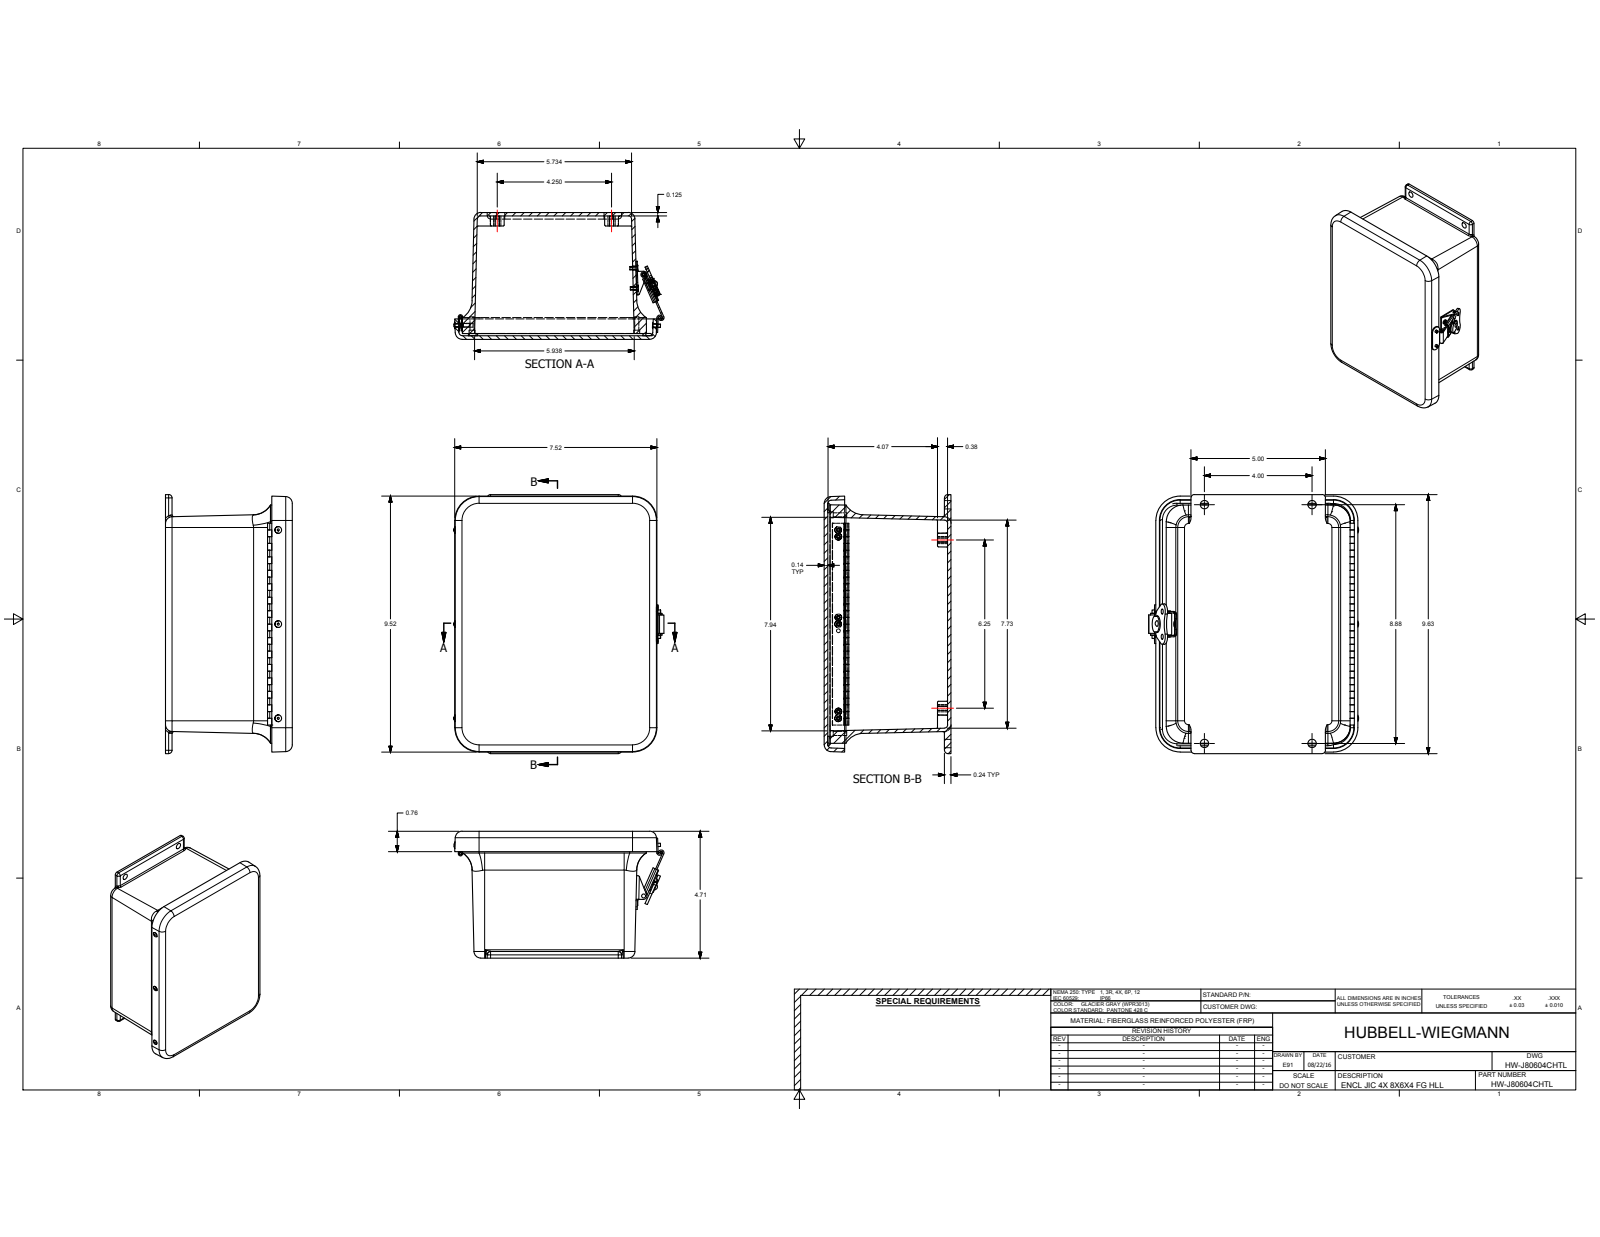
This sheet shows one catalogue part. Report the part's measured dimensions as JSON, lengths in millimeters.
{"part_name": "HW-J806CHTL; WP806H&LBOX; WP806HLU; WP806HCVR (+8 more)", "step_written_by": "Autodesk Inventor 2017 (CONFIG_CONTROL_DESIGN)", "units": "millimeters", "bodies": {"solids": 30, "faces": 817, "planar": 317, "cylindrical": 327, "other": 173}, "overall_size": [244.6, 198.47, 119.75], "volume_mm3": 727558, "surface_area_mm2": 399845, "round_holes": [[3.56, 11], [2.64, 10], [3.86, 8], [3.33, 6], [4.04, 4], [5.54, 4], [7.92, 4], [3.3, 2], [3.38, 2], [4.75, 2], [1.7, 1], [2.16, 1]], "round_bosses_or_shafts": [[3.17, 10], [6.86, 4], [16.76, 1], [14.78, 1], [13.34, 1], [7.26, 1], [5.41, 1], [4.57, 1]], "partial_cylinders_radius": [[0.79, 36], [3.17, 17], [6.35, 9], [0.38, 8], [1.88, 8], [1.52, 7], [0.29, 4], [0.51, 4]], "face_to_face_distances": [3.18, 3.42, 116.33, 119.75, 3.17, 113.15, 116.57, 3.43, 114.3, 111.12], "hole_center_spacings": [88.9, 191.98, 33.48, 184.12, 192.12, 218.8, 33.68, 76.2]}
